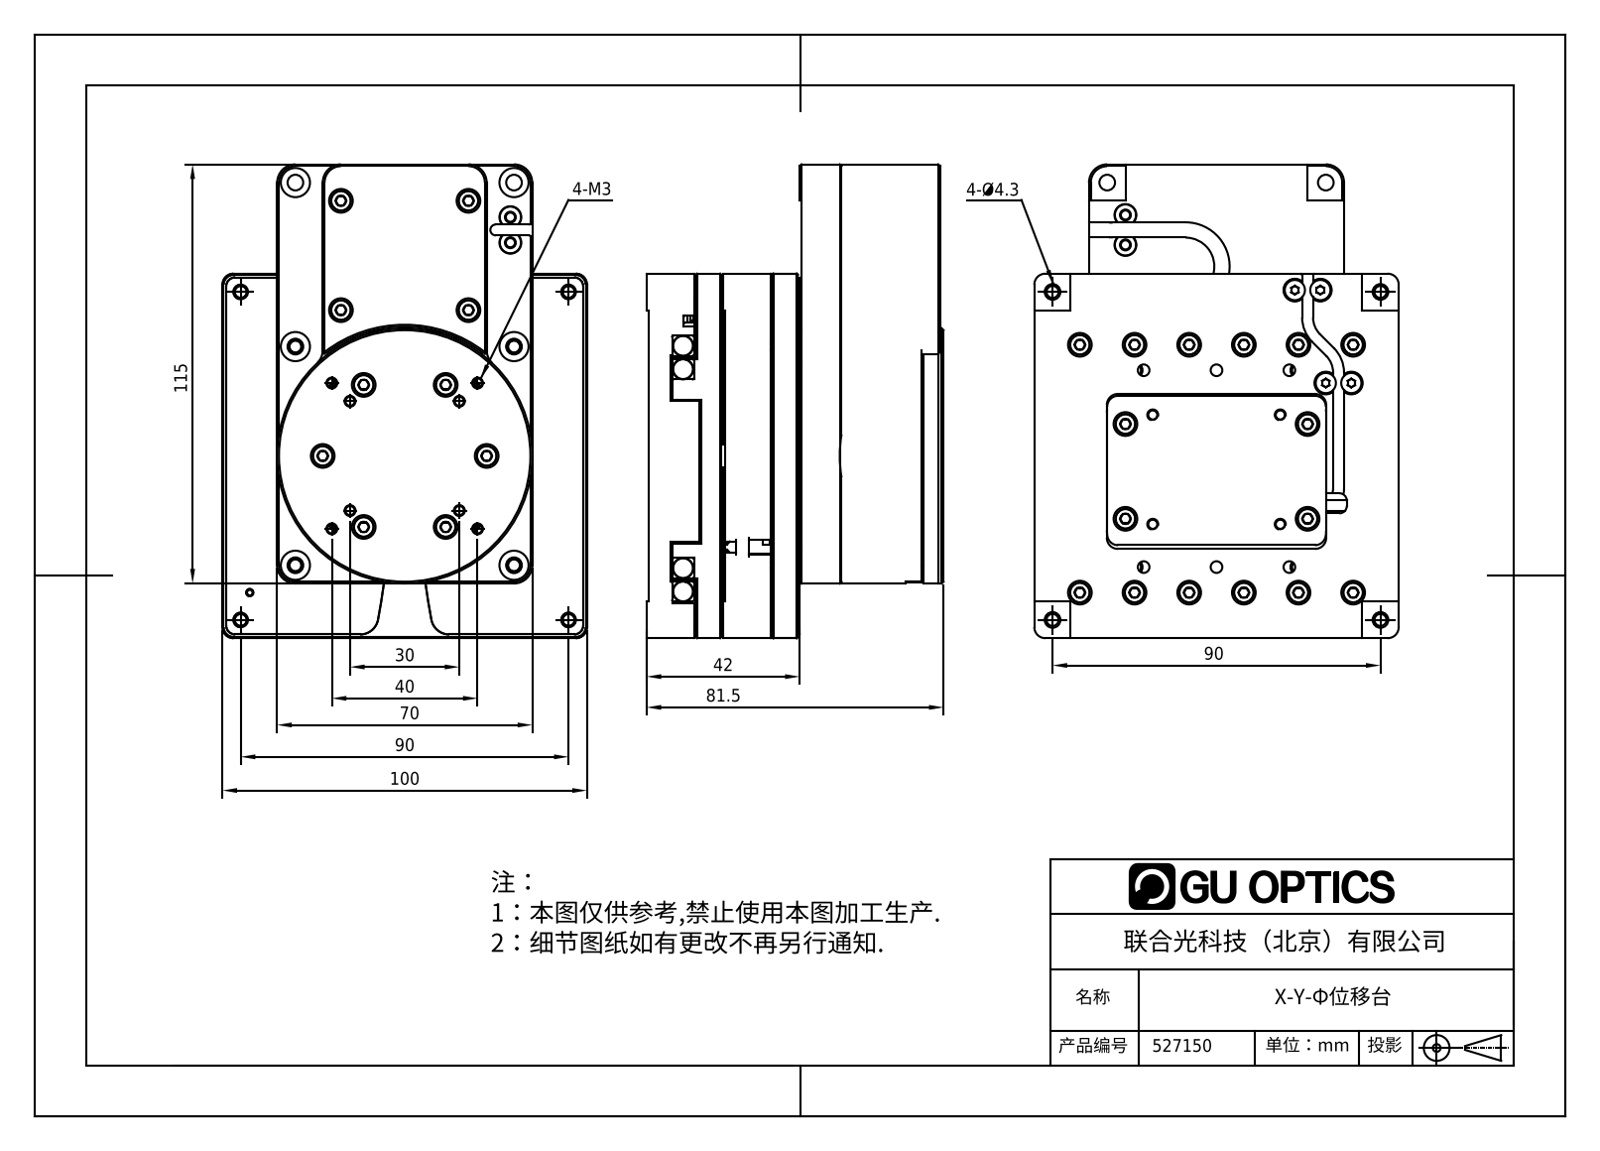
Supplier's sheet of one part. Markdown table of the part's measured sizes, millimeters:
| quantity | value |
| --- | --- |
| STEP written by | SolidWorks 2016 (CONFIG_CONTROL_DESIGN) |
| units | millimeters |
| bodies | 0 solids, 7949 faces (4354 planar, 1977 cylindrical, 1618 other) |
| overall size | 130 × 100 × 81.4 |
| round holes (diameter × count) | 2.5 × 67, 3.2 × 56, 2.55 × 47, 4.4 × 47, 1.6 × 46, 6.5 × 37, 2.05 × 12, 4.3 × 10, 8 × 10, 3 × 9, 3.3 × 8, 6.2 × 7 |
| round bosses / shafts (diameter × count) | 2 × 110, 3 × 90, 5.5 × 34, 3.8 × 24, 2.5 × 24, 2.46 × 20, 1.57 × 18, 2.46 × 17 |
| partial cylindrical surfaces (radius × count) | 1.5 × 62, 3 × 60, 2 × 32, 5 × 16, 0.5 × 10, 1 × 10, 6.5 × 6, 2.5 × 4 |
| main face-to-face distances | 21, 6.5, 0.5, 14.5, 8, 6, 20.5, 27.5, 14, 15 |
| hole center spacings | 15, 30, 16.55, 62.82, 45, 30.81, 67.98, 60 |
